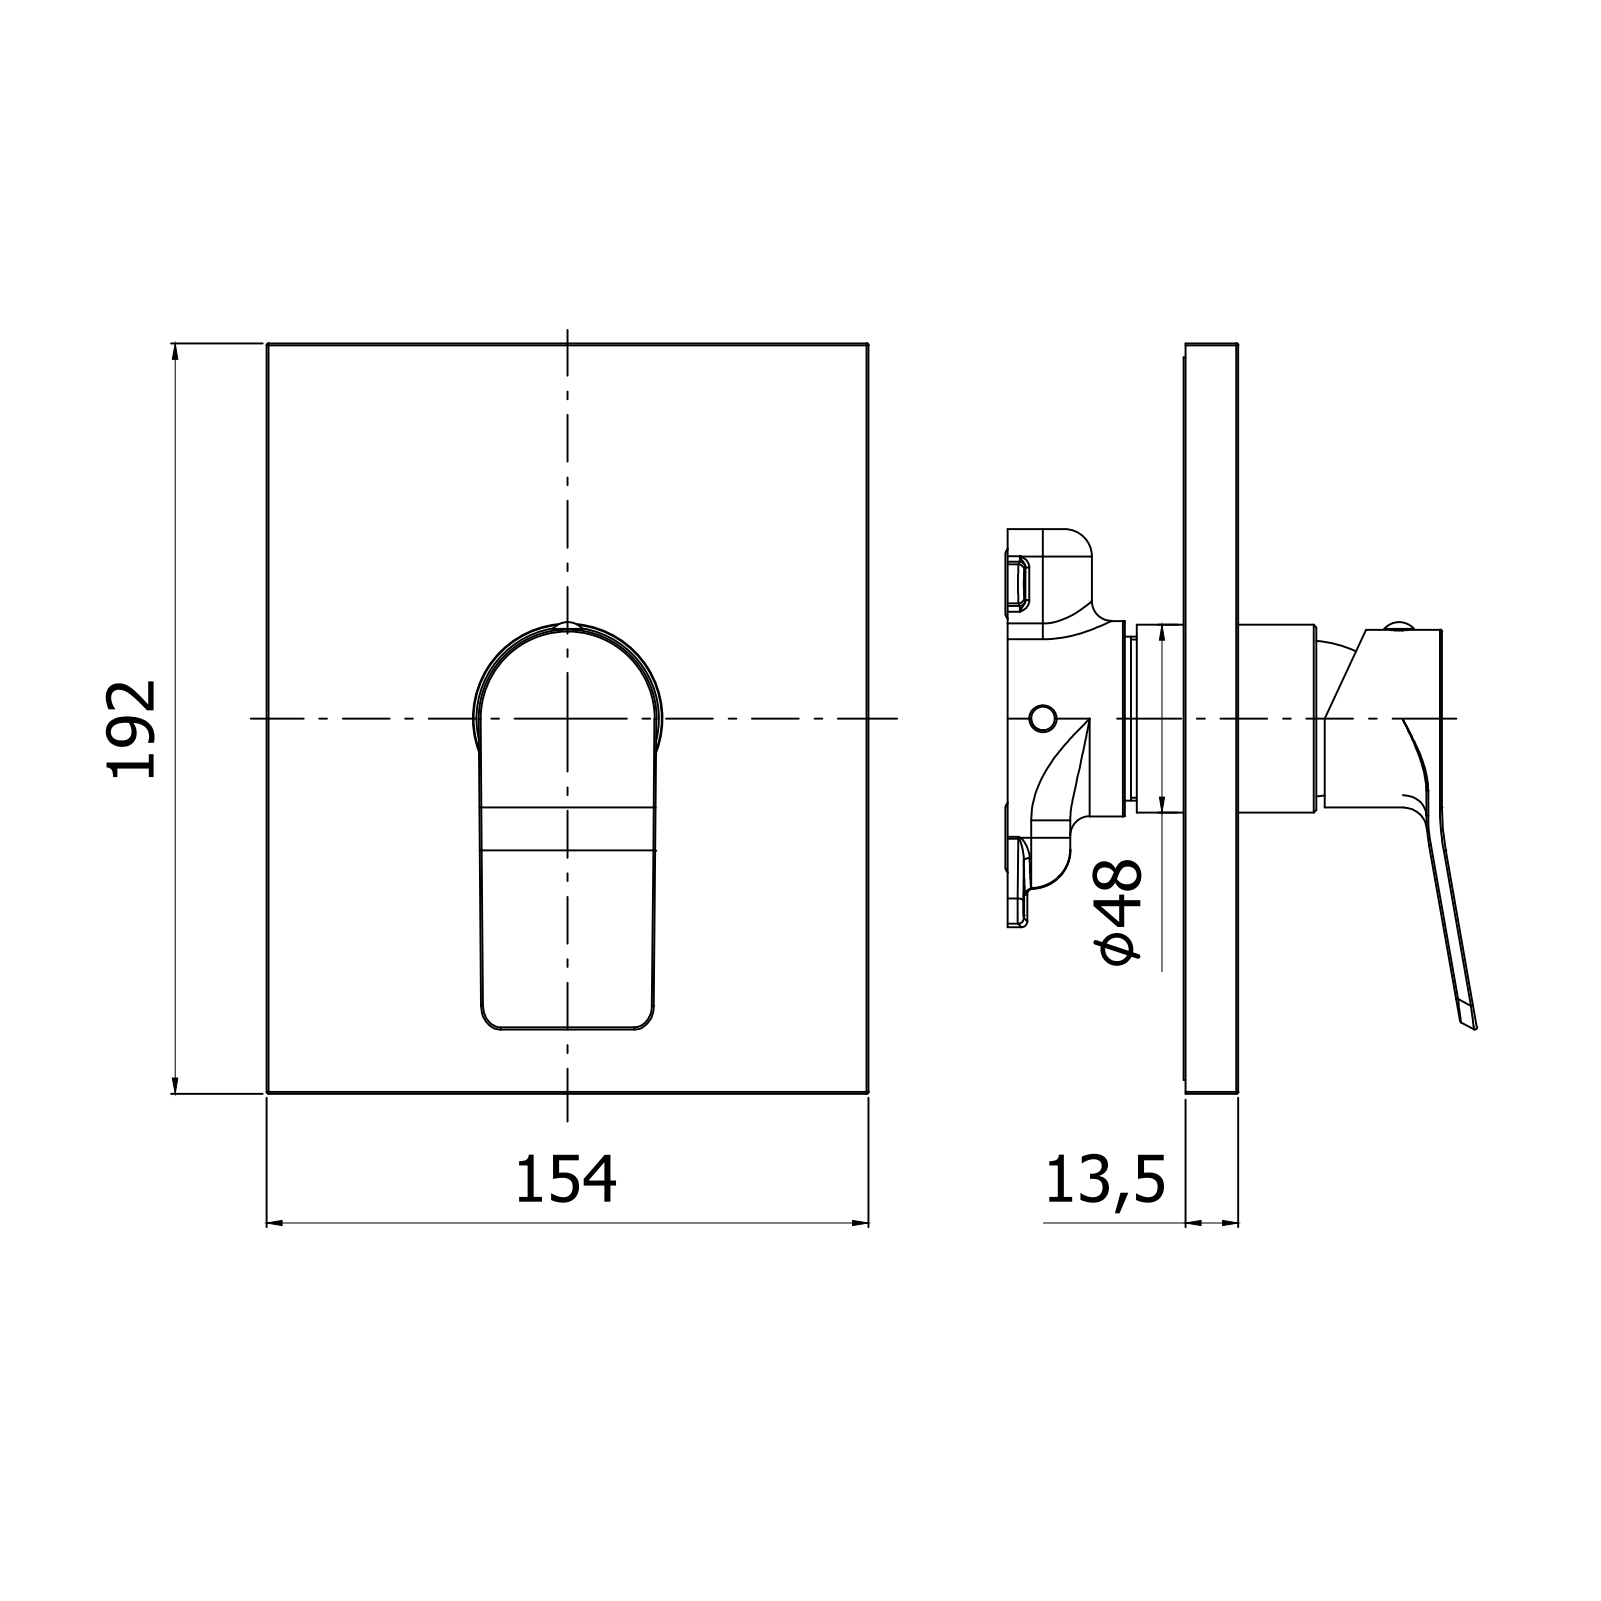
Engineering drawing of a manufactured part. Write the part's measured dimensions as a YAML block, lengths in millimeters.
part_name: "TIBOX010CR"
step_written_by: "CREO PARAMETRIC BY PTC INC, 2020044 (CONFIG_CONTROL_DESIGN)"
units: millimeters
bodies: {solids: 2, faces: 157, planar: 50, cylindrical: 58, other: 49}
overall_size: [192, 154, 74.55]
volume: 441446
surface_area: 93797
round_holes:
  - {diameter: 3, count: 1}
  - {diameter: 4.2, count: 1}
  - {diameter: 5.5, count: 1}
  - {diameter: 30.6, count: 1}
  - {diameter: 36, count: 1}
  - {diameter: 37.5, count: 1}
round_bosses_or_shafts:
  - {diameter: 48.1, count: 1}
  - {diameter: 45.5, count: 1}
  - {diameter: 7.6, count: 1}
partial_cylinders:
  - {radius: 0.5, count: 18}
  - {radius: 1.5, count: 2}
  - {radius: 5, count: 2}
  - {radius: 44.14, count: 1}
  - {radius: 63, count: 1}
face_to_face_distances: [13.5, 154, 192, 4.01, 65.6, 52.1, 61.6, 48.1, 4, 20]
